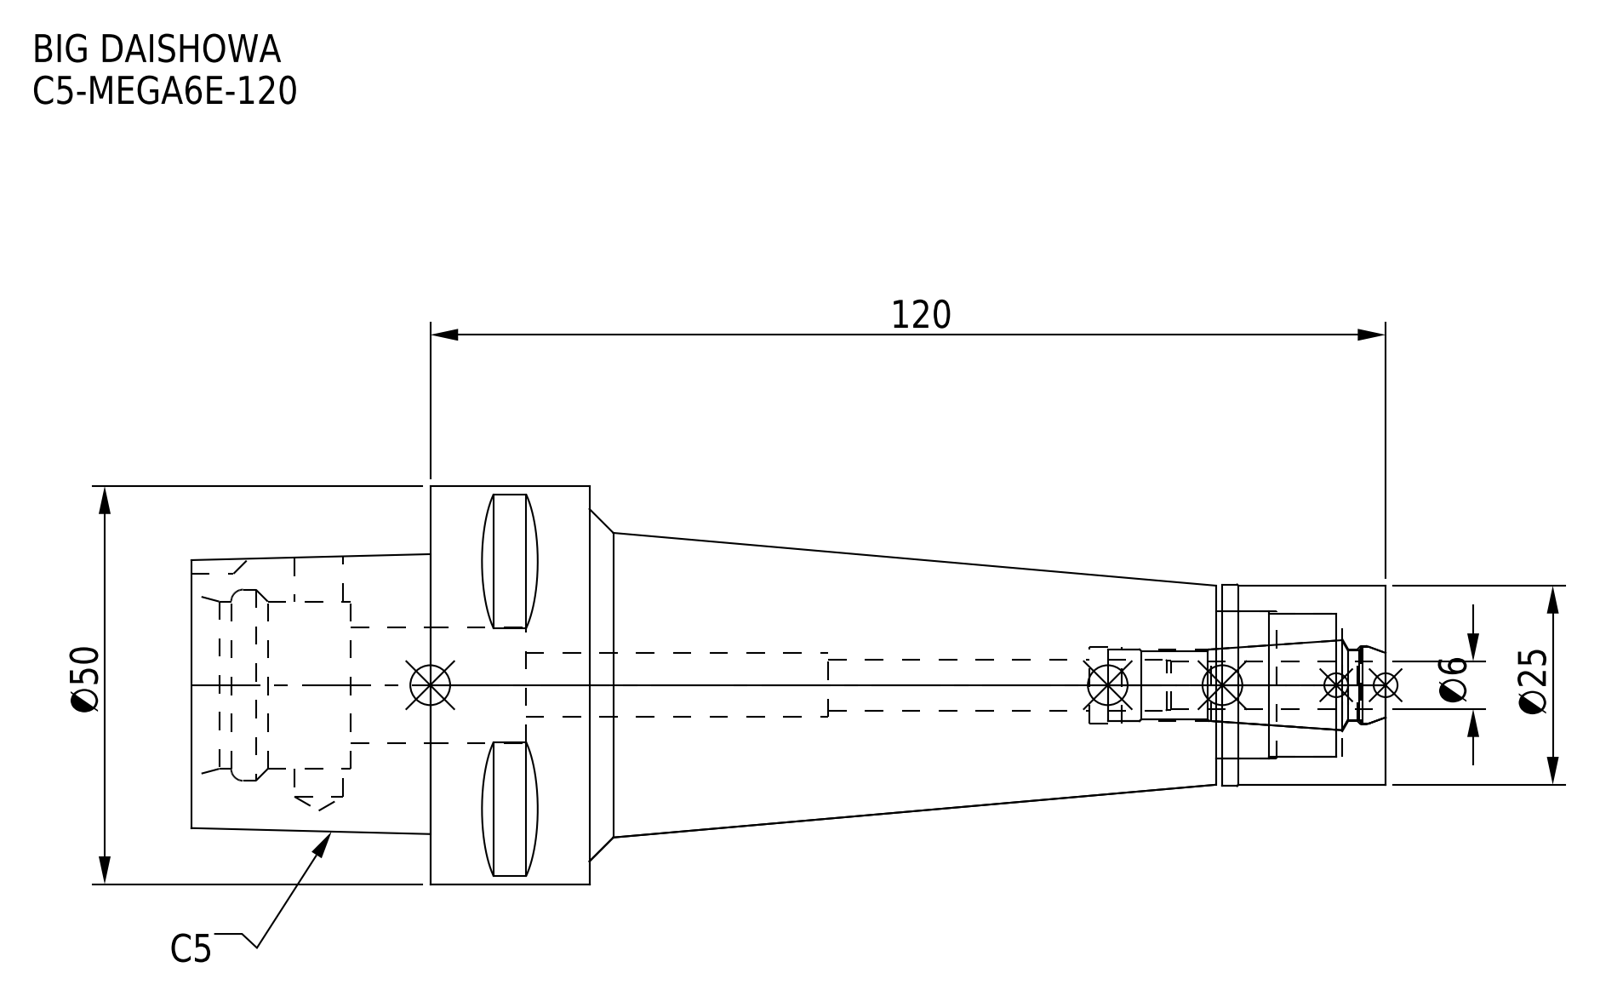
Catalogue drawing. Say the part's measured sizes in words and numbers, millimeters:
The part is named "C5-MEGA6E-120-060_ASM.stp; C5-MEGA6E-120-060.stp; C5-MEGA6E-120-060-FreeParts; DXF_TEMP_ASSY_ASM_4_ASM.stp (+3 more)". Its 3-D file was written by "SolidWorks 2019 (CONFIG_CONTROL_DESIGN)". It is 2 solids with 100 faces: 37 planar, 39 cylindrical and 24 other. Overall it measures 150 by 50 by 50 millimeters. Its volume is 123 326 cubic millimeters and its surface area 26 867 square millimeters. Round holes: 1 of diameter 6.1, 1 of diameter 6.4, 1 of diameter 8, 1 of diameter 9, 1 of diameter 9.6, 1 of diameter 9.9, 1 of diameter 14.5, 1 of diameter 18, 1 of diameter 18.5, 1 of diameter 21, 1 of diameter 24. Round bosses or shafts: 1 of diameter 50, 1 of diameter 25.3, 1 of diameter 25. Partial cylindrical surfaces (rounded edges, fillets, slot ends): 1 of radius 4. The main face-to-face distances are 20, 30, 120, 100, 50, 150, 20.5, 79.5, 99.5, 129.5.
